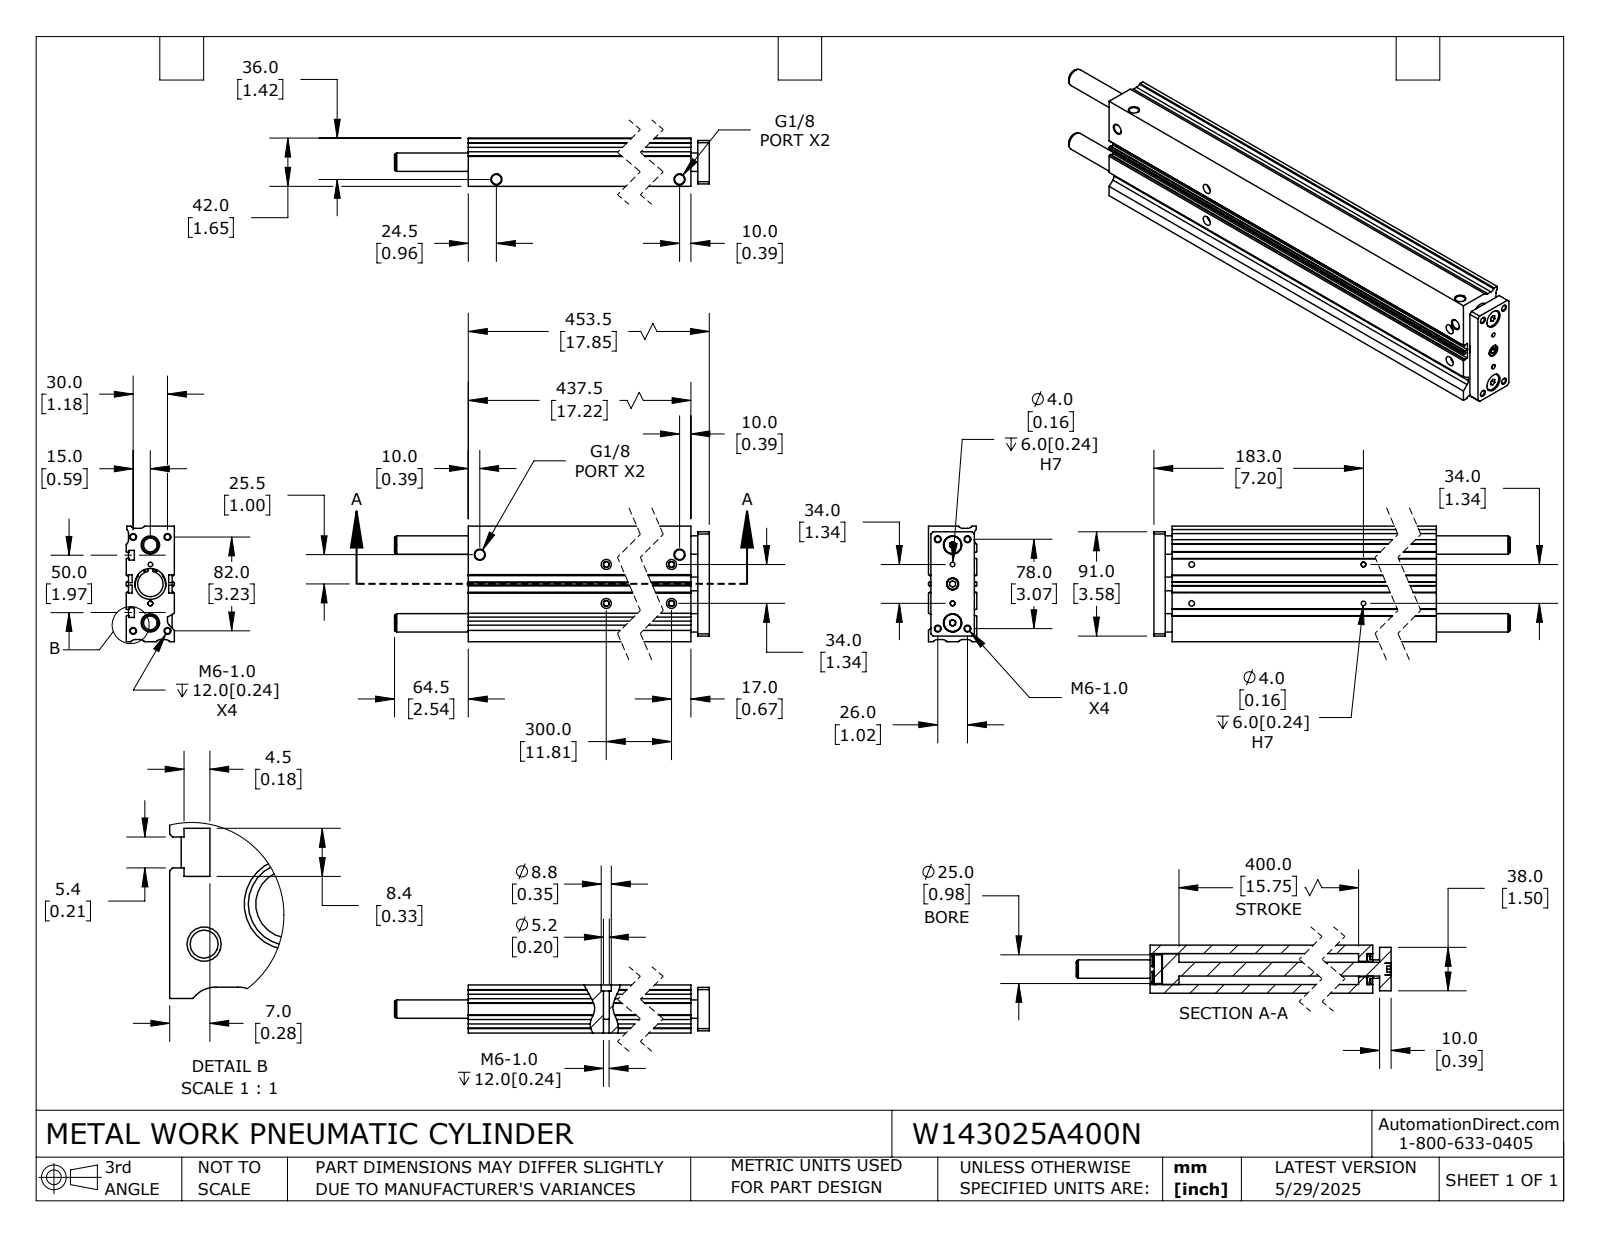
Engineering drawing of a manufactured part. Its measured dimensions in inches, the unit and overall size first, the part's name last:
Units: inches
Overall size (bounding box): 20.394 × 3.976 × 1.654
Round holes (diameter × count): ⌀0.194 ×6, ⌀0.194 ×6, ⌀0.067 ×4, ⌀0.157 ×4, ⌀0.205 ×4, ⌀0.337 ×4, ⌀0.346 ×4, ⌀0.63 ×2, ⌀0.413 ×1, ⌀0.472 ×1, ⌀0.539 ×1, ⌀0.874 ×1
Round bosses / shafts (diameter × count): ⌀0.61 ×2, ⌀1.063 ×1, ⌀0.984 ×1, ⌀0.65 ×1, ⌀0.394 ×1
Partial cylindrical surfaces — rounded edges, fillets, slot ends (radius × count): R0.039 ×12, R0.197 ×9, R0.079 ×8, R0.524 ×2, R0.559 ×1
Main face-to-face distances: 1.654, 0.079, 0.197, 1.457, 1.378, 0.839, 3.976, 2.299, 0.276, 0.354
Hole centre spacings: 1.339, 0.111, 0.29, 0.5, 0.548, 0.652, 0.669, 0.902
Volume: 95.22 in³ · Surface area: 533.5 in²
Bodies: 6 solids, 390 faces (191 planar, 157 cylindrical, 42 other)
Part name (STEP PRODUCT): W143025A400N; W143025A400N_BODY; W143025A400N_ROD
STEP written by: SolidWorks 2024 (CONFIG_CONTROL_DESIGN)
